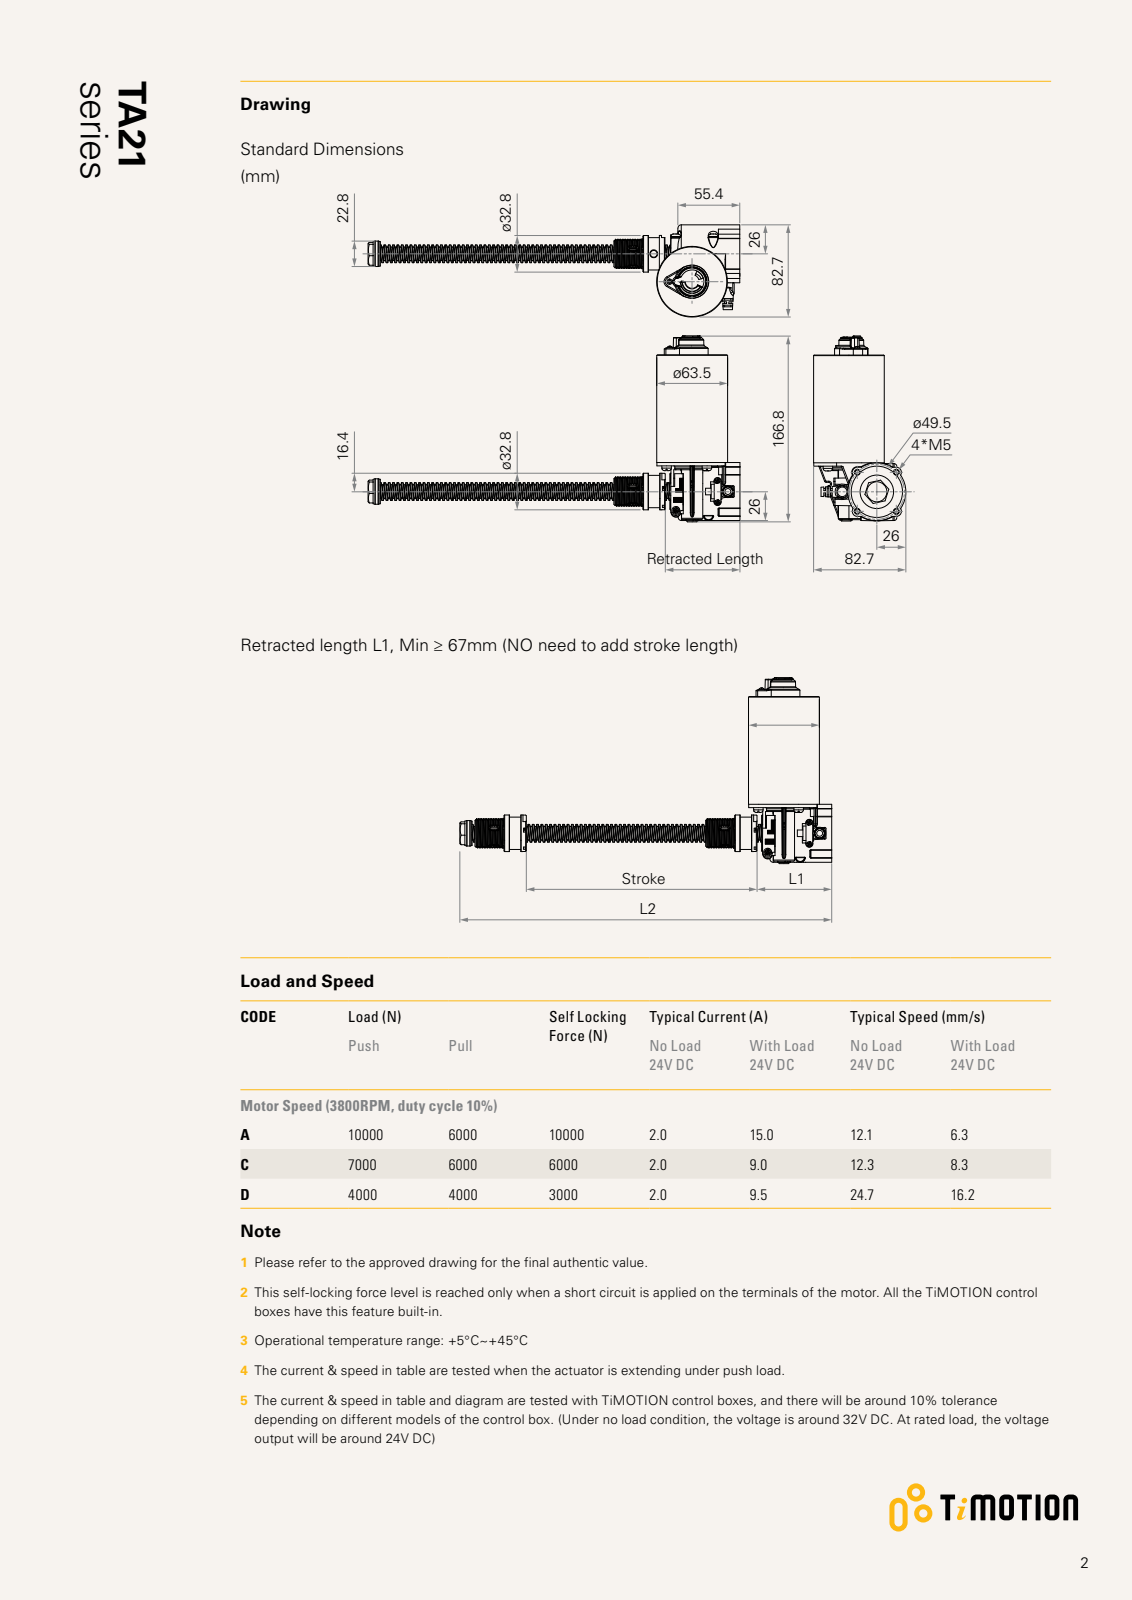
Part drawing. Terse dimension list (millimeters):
name: 三維產品模型圖-iA21-A
written by: SolidWorks 2015 (CONFIG_CONTROL_DESIGN)
unit: mm
bodies: 1 solid, 877 faces (286 planar, 383 cylindrical, 208 other)
size: 529.08 × 164.1 × 82.65
volume: 550 753 mm³; area: 87 140 mm²
holes: 4× ⌀4.3, 2× ⌀5.2, 1× ⌀24, 1× ⌀30
bosses: 6× ⌀8.5, 1× ⌀63.3, 1× ⌀63, 1× ⌀52, 1× ⌀34, 1× ⌀32.8, 1× ⌀29, 1× ⌀25.8
rounds: 24× R0.5, 15× R1, 5× R4.5, 4× R0.2, 4× R4.6, 3× R1.5, 2× R1.25, 2× R4
face distances: 99.6, 404.2, 466, 61.8, 46, 5, 3.5, 147.6, 48, 15.5
hole spacings: 24.75, 35, 49.5, 39.83
